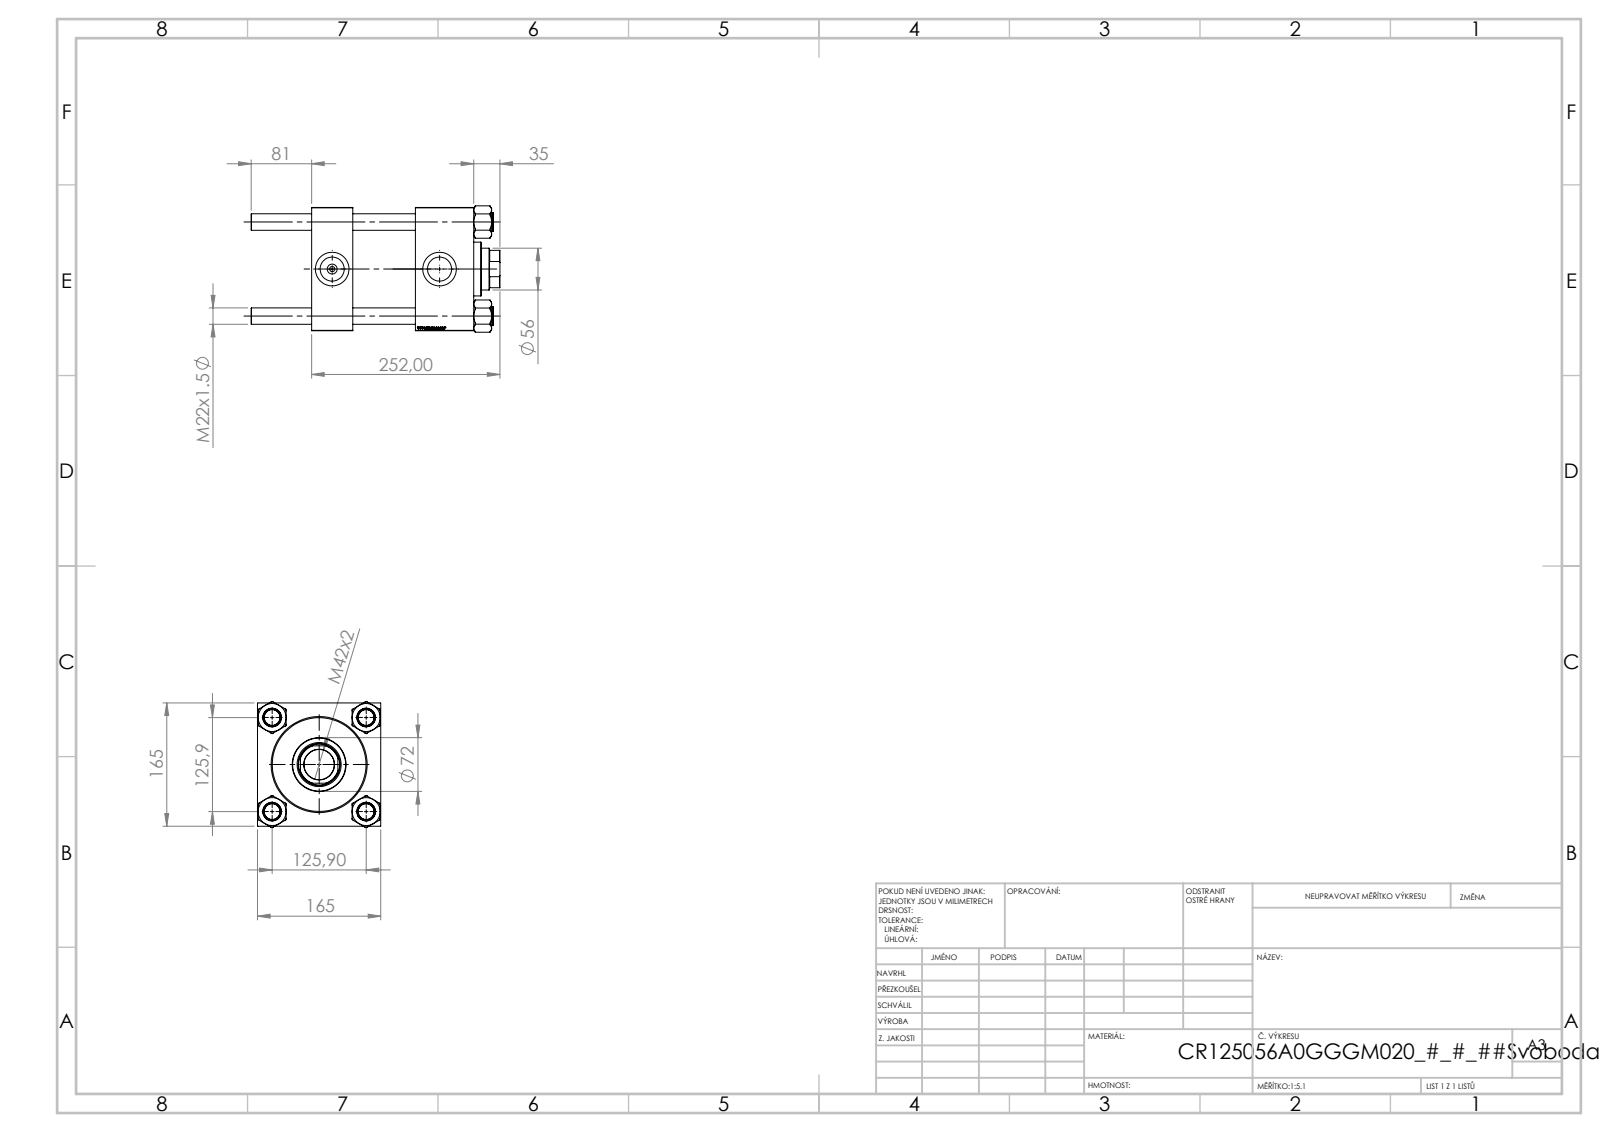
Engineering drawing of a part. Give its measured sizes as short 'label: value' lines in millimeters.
name: CR025_012_A_0_G_A_G_M_020_+#_##_TYCINKA; V215_VC_A; V215CR_BODY_A; NUT_M5 (+1 more)
written by: SolidWorks 2019 (CONFIG_CONTROL_DESIGN)
unit: mm
bodies: 11 solids, 1182 faces (567 planar, 79 cylindrical, 536 other)
size: 333 × 169.14 × 165
volume: 4 677 000 mm³; area: 550 041 mm²
holes: 4× ⌀22, 2× ⌀7, 2× ⌀32.24, 2× ⌀45, 1× ⌀40.5, 1× ⌀56, 1× ⌀59, 1× ⌀96, 1× ⌀125, 1× ⌀125.5
bosses: 4× ⌀25, 1× ⌀131, 1× ⌀72
rounds: 1× R27
face distances: 165, 55, 162, 217, 139, 84, 78, 188.3, 133.3, 49.3
hole spacings: 89.02, 125.9, 178.05, 143.74
